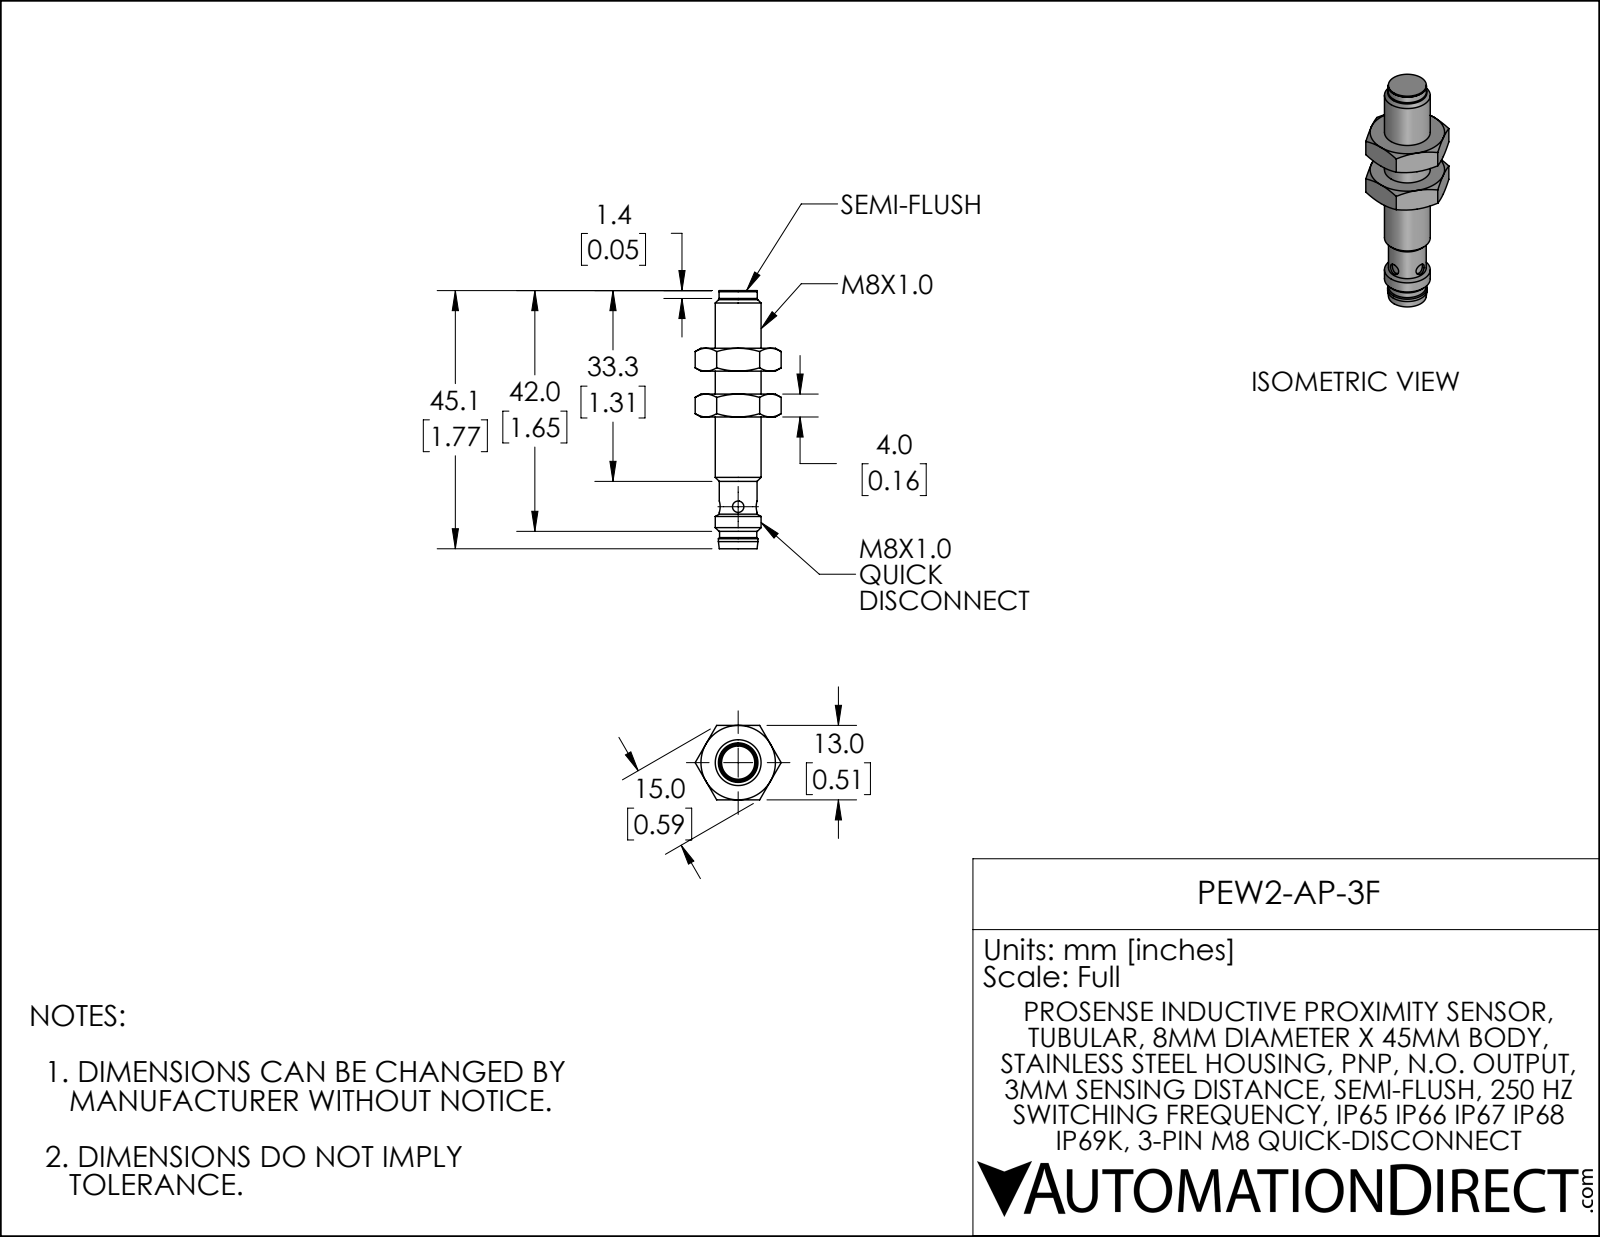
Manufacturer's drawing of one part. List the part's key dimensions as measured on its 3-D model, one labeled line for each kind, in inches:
Part name (STEP PRODUCT): PEW2-AP-3F
STEP written by: SolidWorks 2019 (CONFIG_CONTROL_DESIGN)
Units: inches
Bodies: 3 solids, 75 faces (21 planar, 18 cylindrical, 36 other)
Overall size (bounding box): 1.774 × 0.591 × 0.512
Volume: 0.17 in³ · Surface area: 3.41 in²
Round holes (diameter × count): ⌀0.079 ×2, ⌀0.272 ×1
Round bosses / shafts (diameter × count): ⌀0.315 ×1, ⌀0.272 ×1, ⌀0.263 ×1, ⌀0.261 ×1, ⌀0.26 ×1, ⌀0.256 ×1, ⌀0.228 ×1
Main face-to-face distances: 0.157, 0.512, 0.315, 0.869, 0.711, 0.554, 0.707, 0.864, 1.022, 1.575
